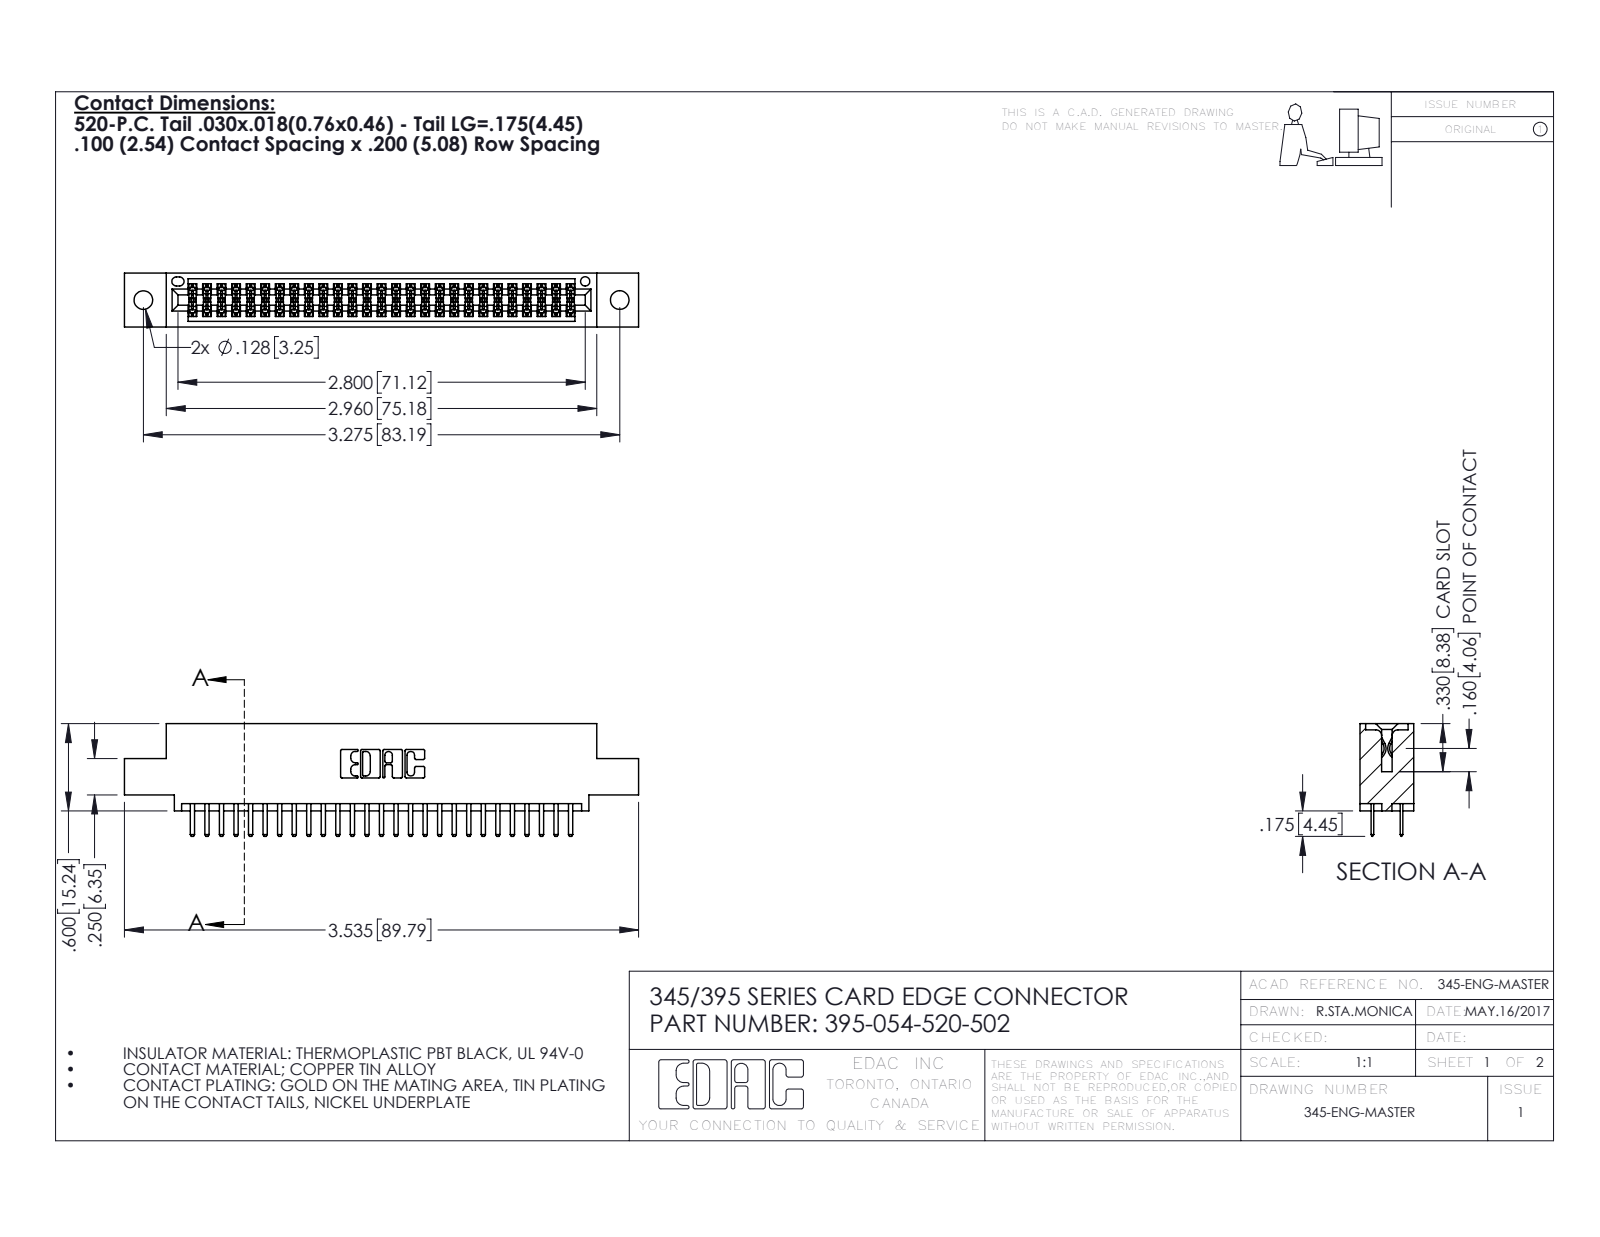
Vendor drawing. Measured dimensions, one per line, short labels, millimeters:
name: 395-054-520-502; 345-292-001_345-293-120; 345 Part_0.110 Offset - 0.128 Dia
written by: SolidWorks 2016 (CONFIG_CONTROL_DESIGN)
unit: mm
bodies: 55 solids, 3046 faces (1974 planar, 1072 cylindrical, 0 other)
size: 89.8 × 19.7 × 9.4
volume: 8 460 mm³; area: 11 970 mm²
holes: 2× ⌀3.3, 1× ⌀1.6
rounds: 81× R0.2, 58× R0.3, 22× R0.3, 6× R0.2, 6× R0.8, 3× R0.7, 2× R0.4, 2× R0.5
face distances: 7.6, 1.8, 5.1, 9.4, 2.5, 6.9, 0.6, 5.7, 0.6, 1.8
hole spacings: 6.9, 77.2, 83.2
